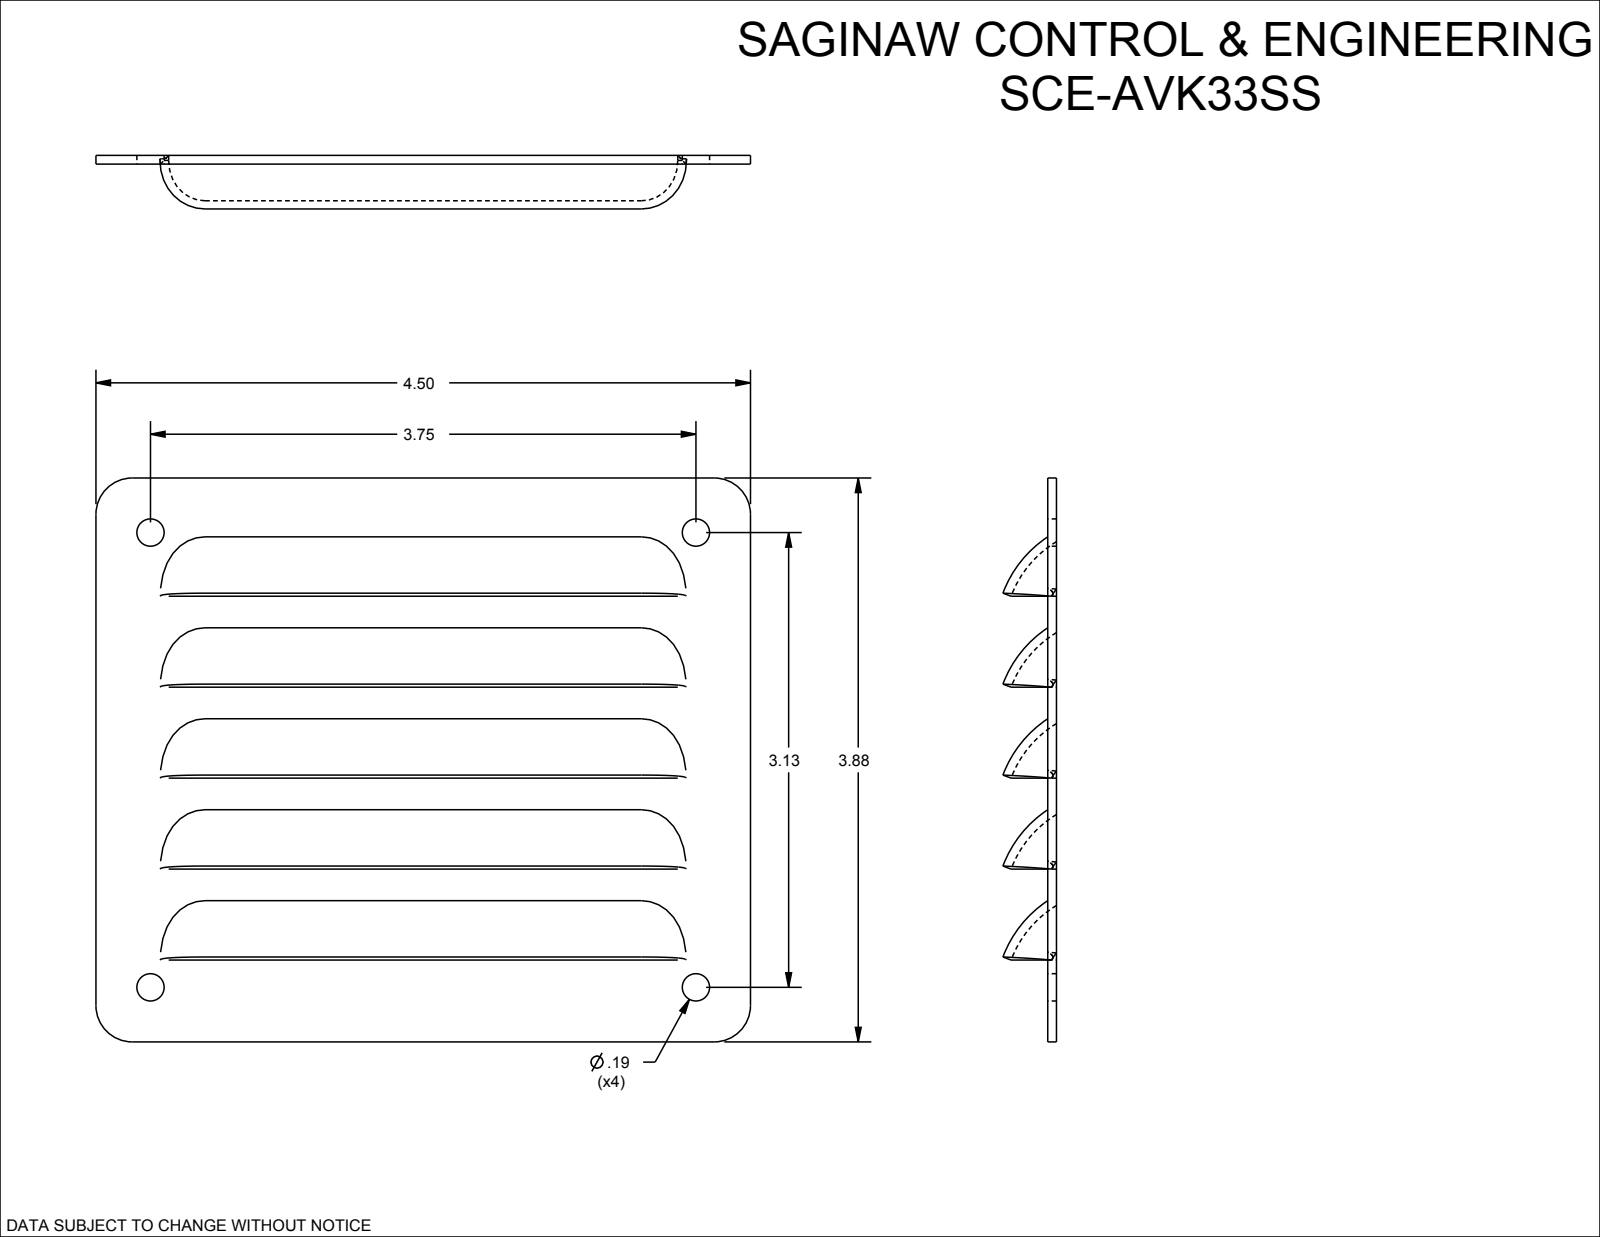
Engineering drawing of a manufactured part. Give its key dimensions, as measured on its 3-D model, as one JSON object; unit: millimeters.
{"part_name": "SCE-AVK33", "step_written_by": "SolidWorks 2021 (AUTOMOTIVE_DESIGN)", "units": "millimeters", "bodies": {"solids": 1, "faces": 91, "planar": 21, "cylindrical": 30, "other": 40}, "overall_size": [114.3, 98.4, 11.9], "volume_mm3": 19520, "surface_area_mm2": 27560, "round_holes": [[4.7, 4]], "partial_cylinders_radius": [[18.8, 5], [20.3, 5], [6.4, 4]], "face_to_face_distances": [1.5, 31.8, 15.9, 15.9, 7.4, 24.4, 29.7, 8.5, 47.6, 63.5], "hole_center_spacings": [79.4, 95.3, 124]}
